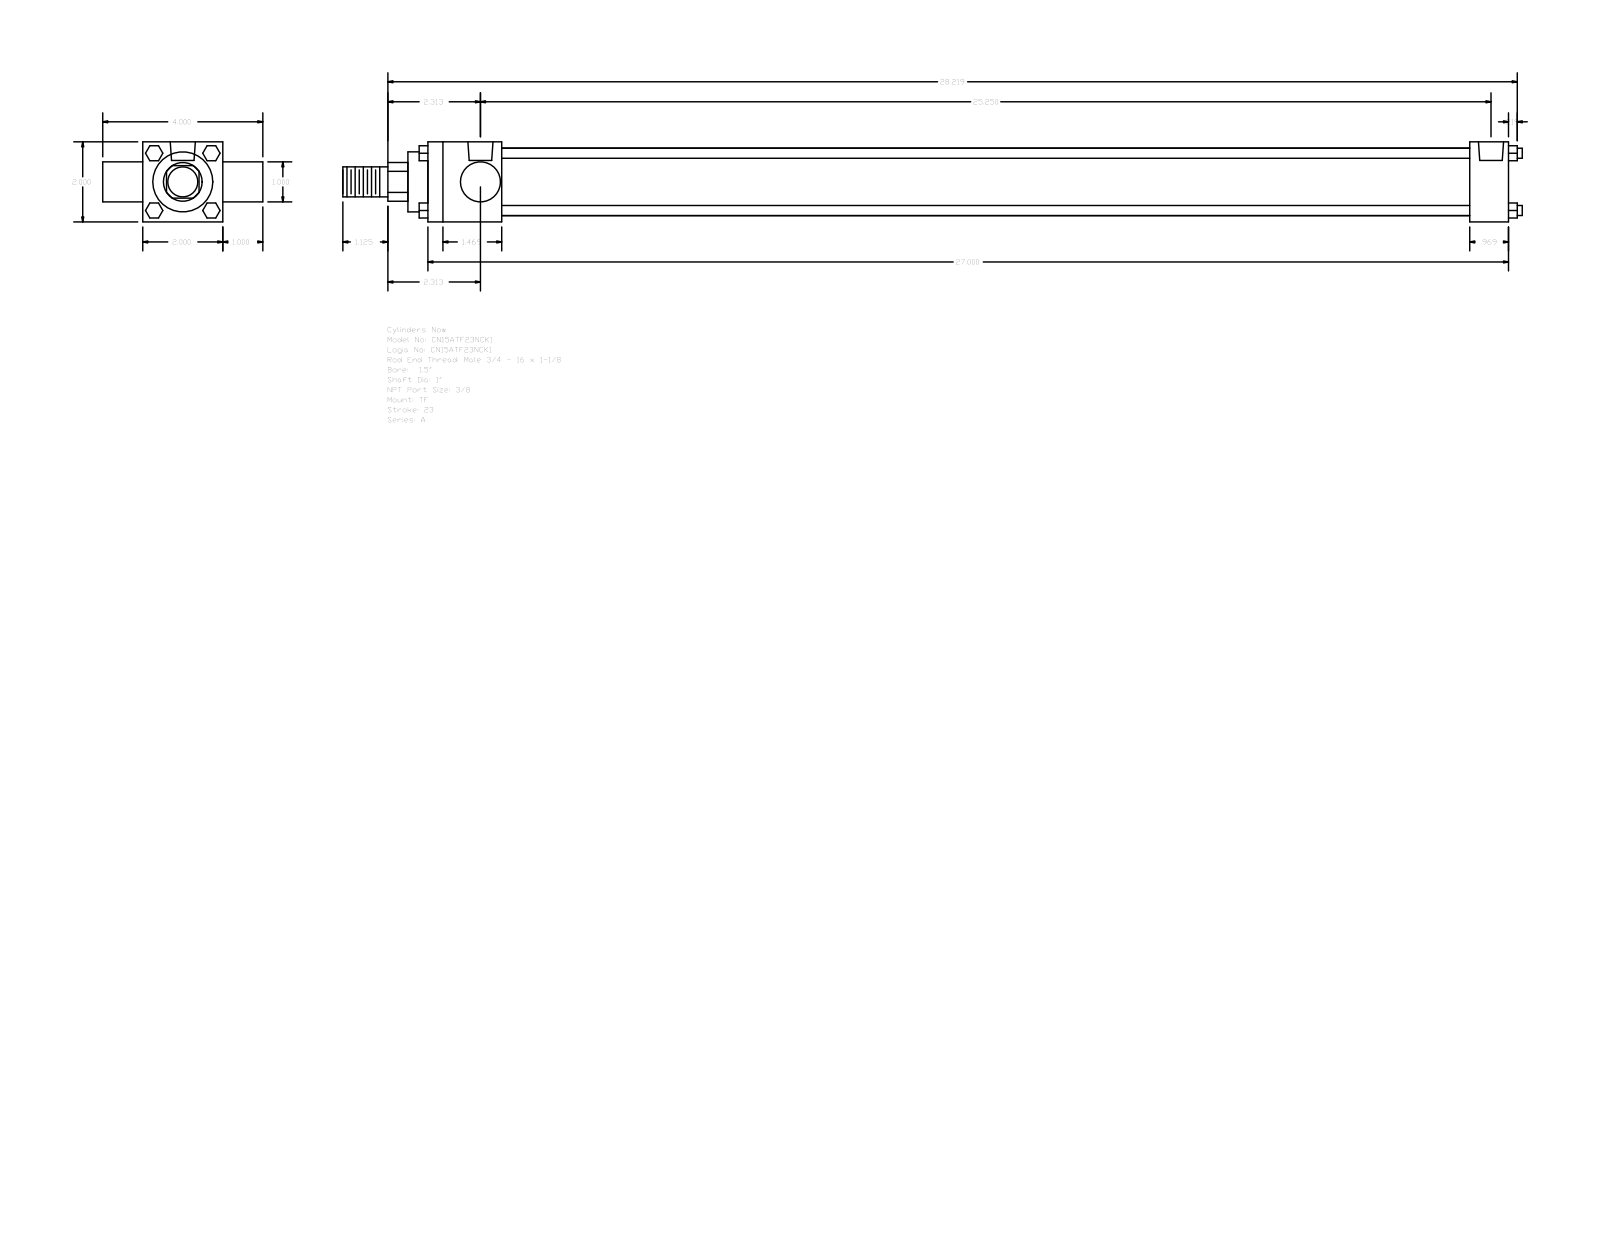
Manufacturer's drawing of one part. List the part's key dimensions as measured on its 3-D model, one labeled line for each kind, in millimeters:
Part name (STEP PRODUCT): A_TF__0150_1
STEP written by: GSSL Pune (CONFIG_CONTROL_DESIGN)
Units: millimetres
Bodies: 0 solids, 120 faces (92 planar, 28 cylindrical, 0 other)
Overall size (bounding box): 748.51 × 101.6 × 50.8
Round holes (diameter × count): ⌀5.56 ×3, ⌀15.93 ×2
Round bosses / shafts (diameter × count): ⌀6.35 ×4, ⌀25.4 ×2, ⌀42.93 ×1, ⌀38.1 ×1, ⌀19.05 ×1
Partial cylindrical surfaces — rounded edges, fillets, slot ends (radius × count): R12.29 ×1
Main face-to-face distances: 50.8, 25.4, 685.8, 76.2, 46.83, 661.19, 614.36, 638.97, 24.61, 12.7
Hole centre spacings: 3.97, 637.38, 633.41, 641.35
